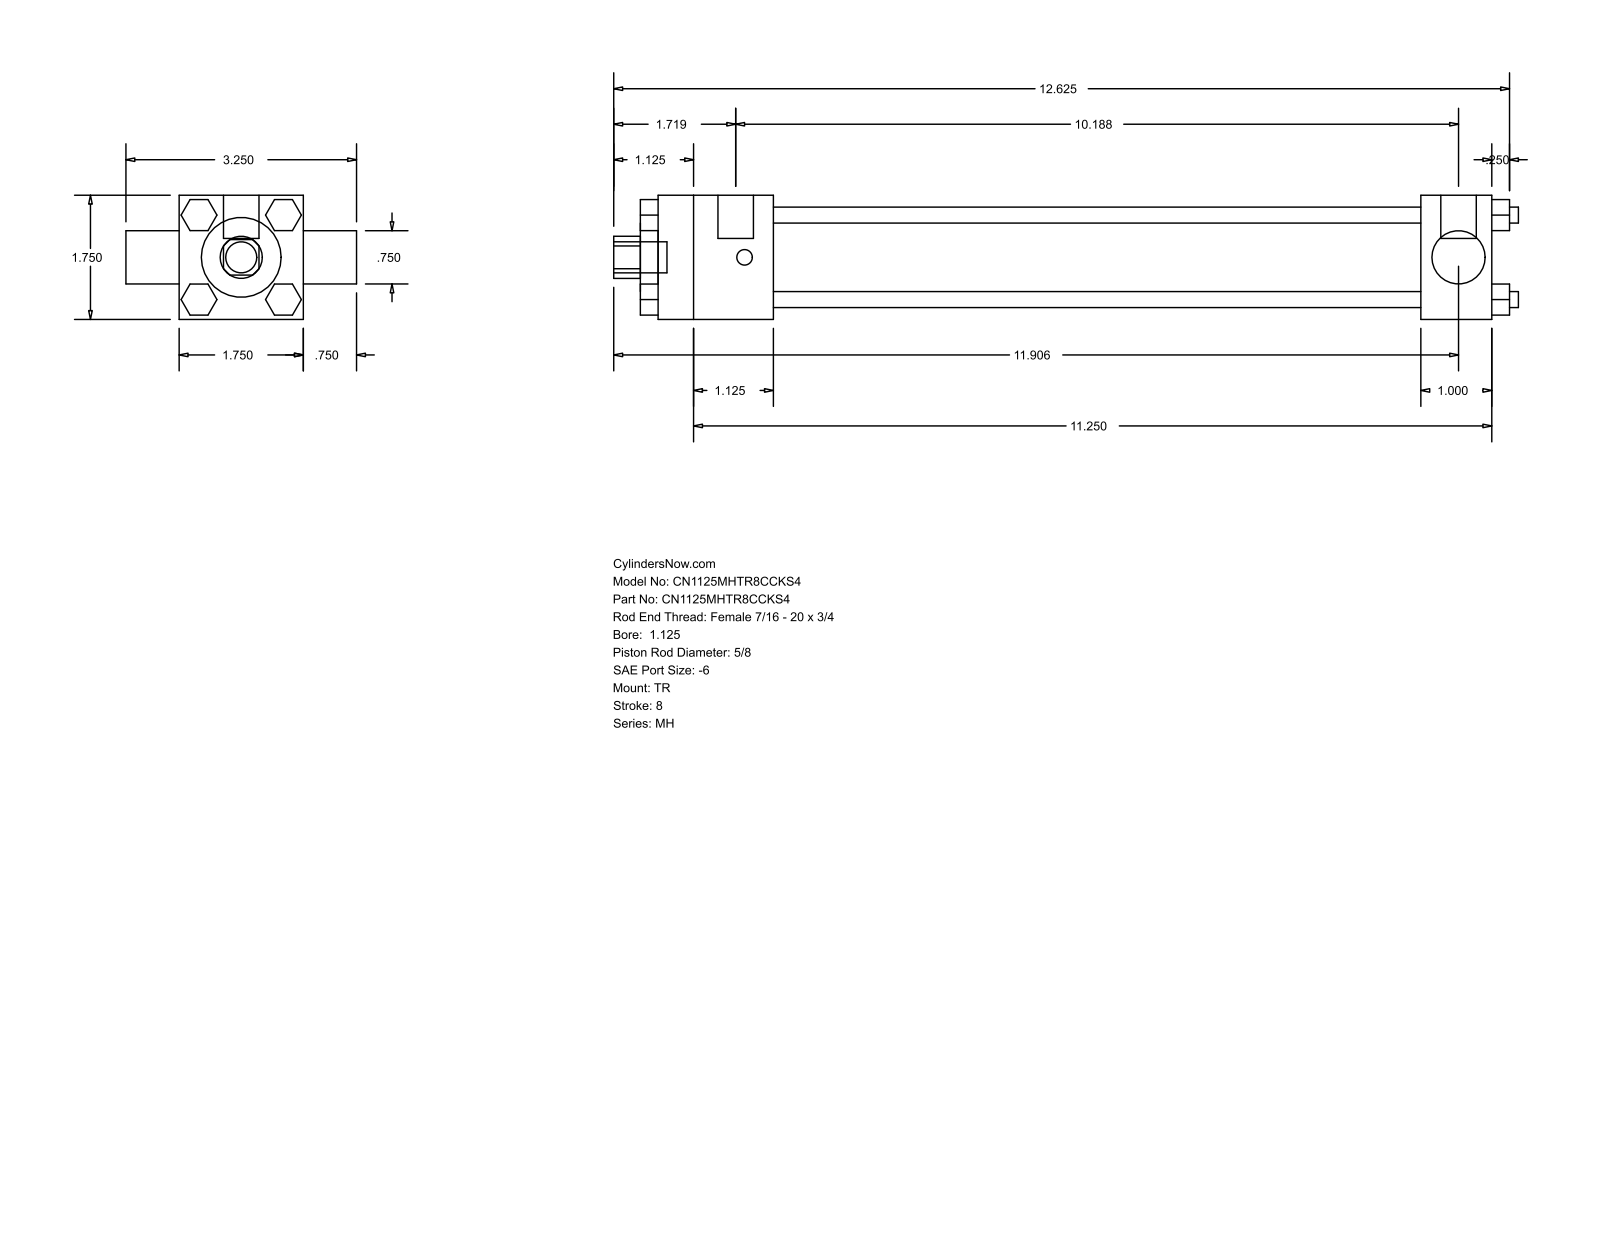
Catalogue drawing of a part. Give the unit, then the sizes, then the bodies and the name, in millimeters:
Units: millimetres
Overall size (bounding box): 323.85 × 82.55 × 44.45
Round holes (diameter × count): ⌀15.88 ×1, ⌀19.05 ×1, ⌀28.57 ×1, ⌀34.92 ×1
Round bosses / shafts (diameter × count): ⌀5.71 ×4, ⌀5.56 ×3, ⌀12.7 ×2, ⌀11.11 ×1
Partial cylindrical surfaces — rounded edges, fillets, slot ends (radius × count): R7.54 ×1
Main face-to-face distances: 44.46, 11.11, 231.78, 257.17, 25.39, 41.27, 273.05, 298.44, 47.62, 6.35
Bodies: 0 solids, 120 faces (92 planar, 28 cylindrical, 0 other)
Part name (STEP PRODUCT): MH_TR__0112_0.625
STEP written by: GSSL Pune (CONFIG_CONTROL_DESIGN)
